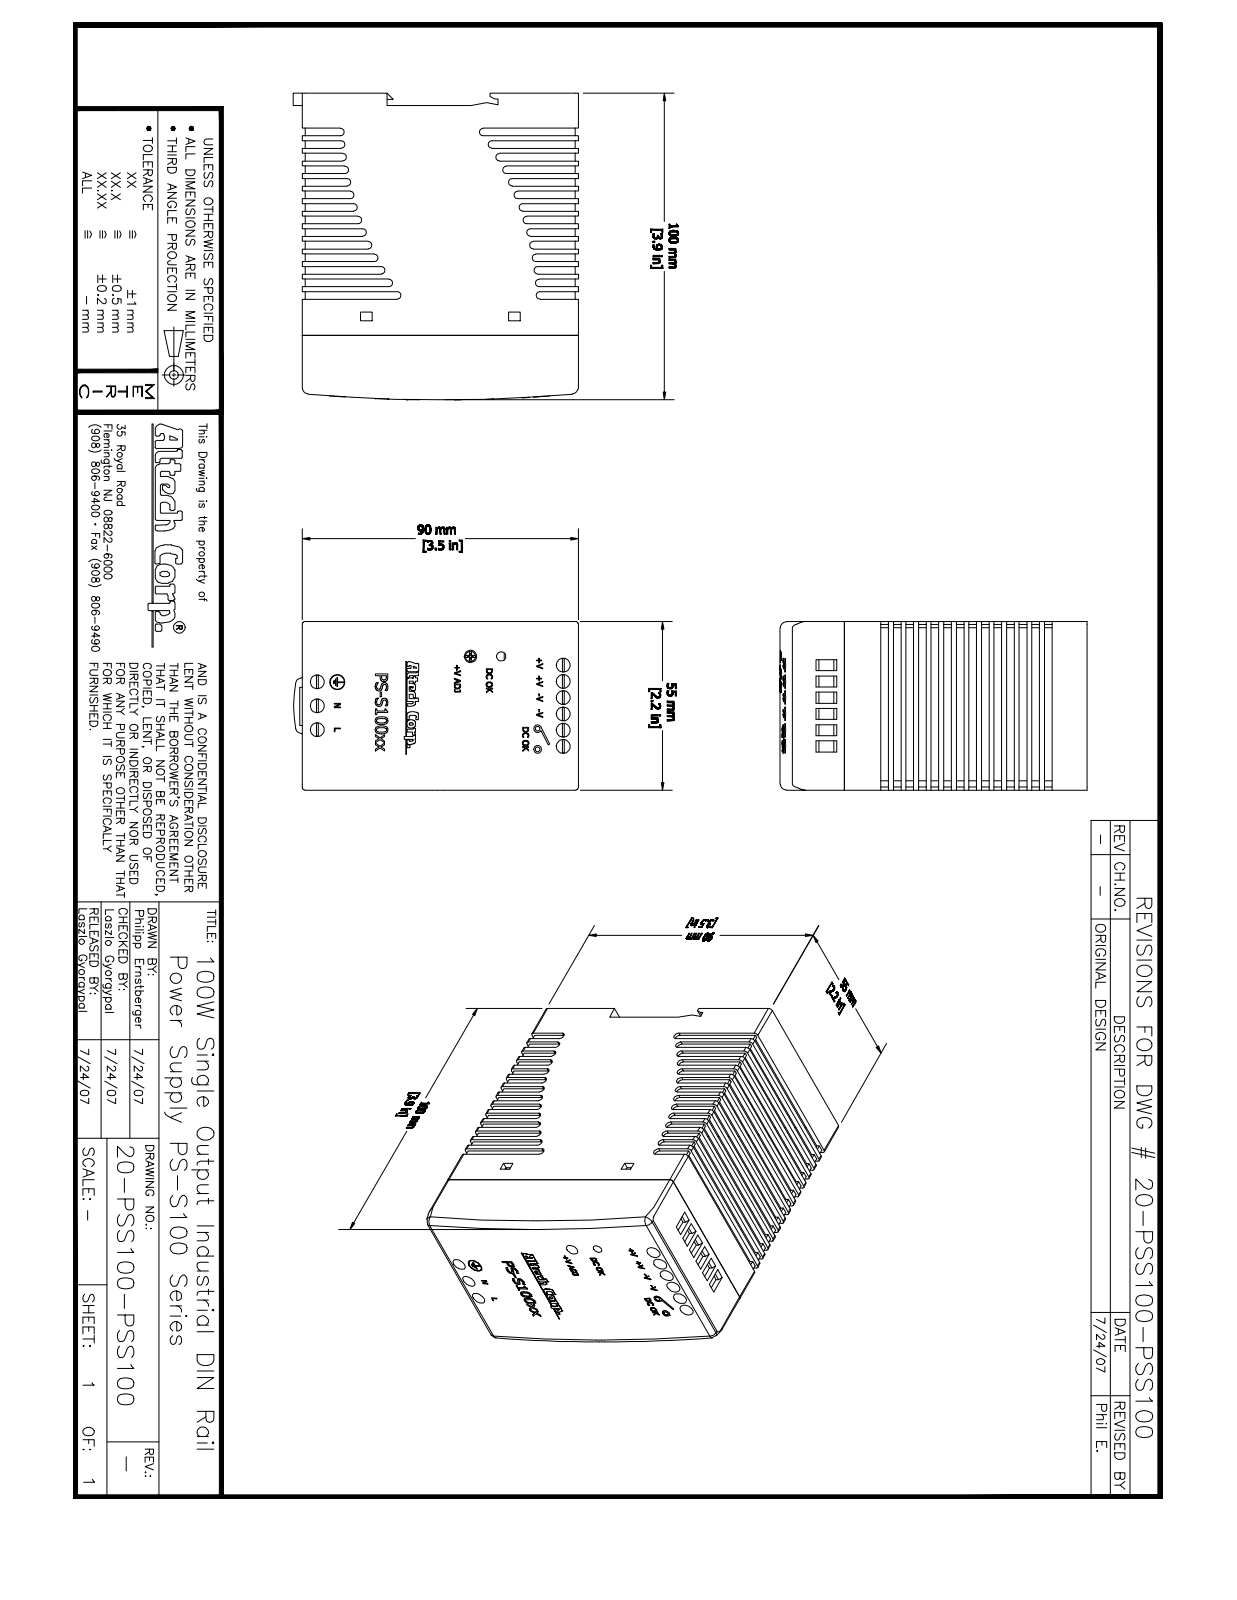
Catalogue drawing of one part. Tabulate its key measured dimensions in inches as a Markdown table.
| quantity | value |
| --- | --- |
| part name | PSS100; box; front; interlock (+2 more) |
| STEP written by | Autodesk Inventor 2008 (AUTOMOTIVE_DESIGN) |
| units | inches |
| bodies | 13 solids, 1396 faces (771 planar, 372 cylindrical, 253 other) |
| overall size | 3.937 × 3.658 × 2.165 |
| volume | 3.973 in³ |
| surface area | 125.4 in² |
| round holes (diameter × count) | 0.177 × 9, 0.059 × 2, 0.118 × 1, 0.157 × 1, 0.181 × 1 |
| round bosses / shafts (diameter × count) | 0.098 × 11, 0.189 × 9, 0.087 × 9, 0.138 × 2, 0.193 × 1, 0.177 × 1, 0.079 × 1 |
| partial cylindrical surfaces (radius × count) | 0.049 × 56, 0.079 × 10, 0.039 × 4, 0.007 × 3, 0.004 × 2, 0.005 × 2, 0.006 × 2, 0.007 × 2 |
| main face-to-face distances | 0.079, 2.087, 2.008, 2.165, 3.465, 0.039, 0.157, 0.161, 3.543, 3.386 |
| hole center spacings | 0.209, 0.417, 0.626, 0.307, 0.835, 3.156, 3.157, 3.163 |
